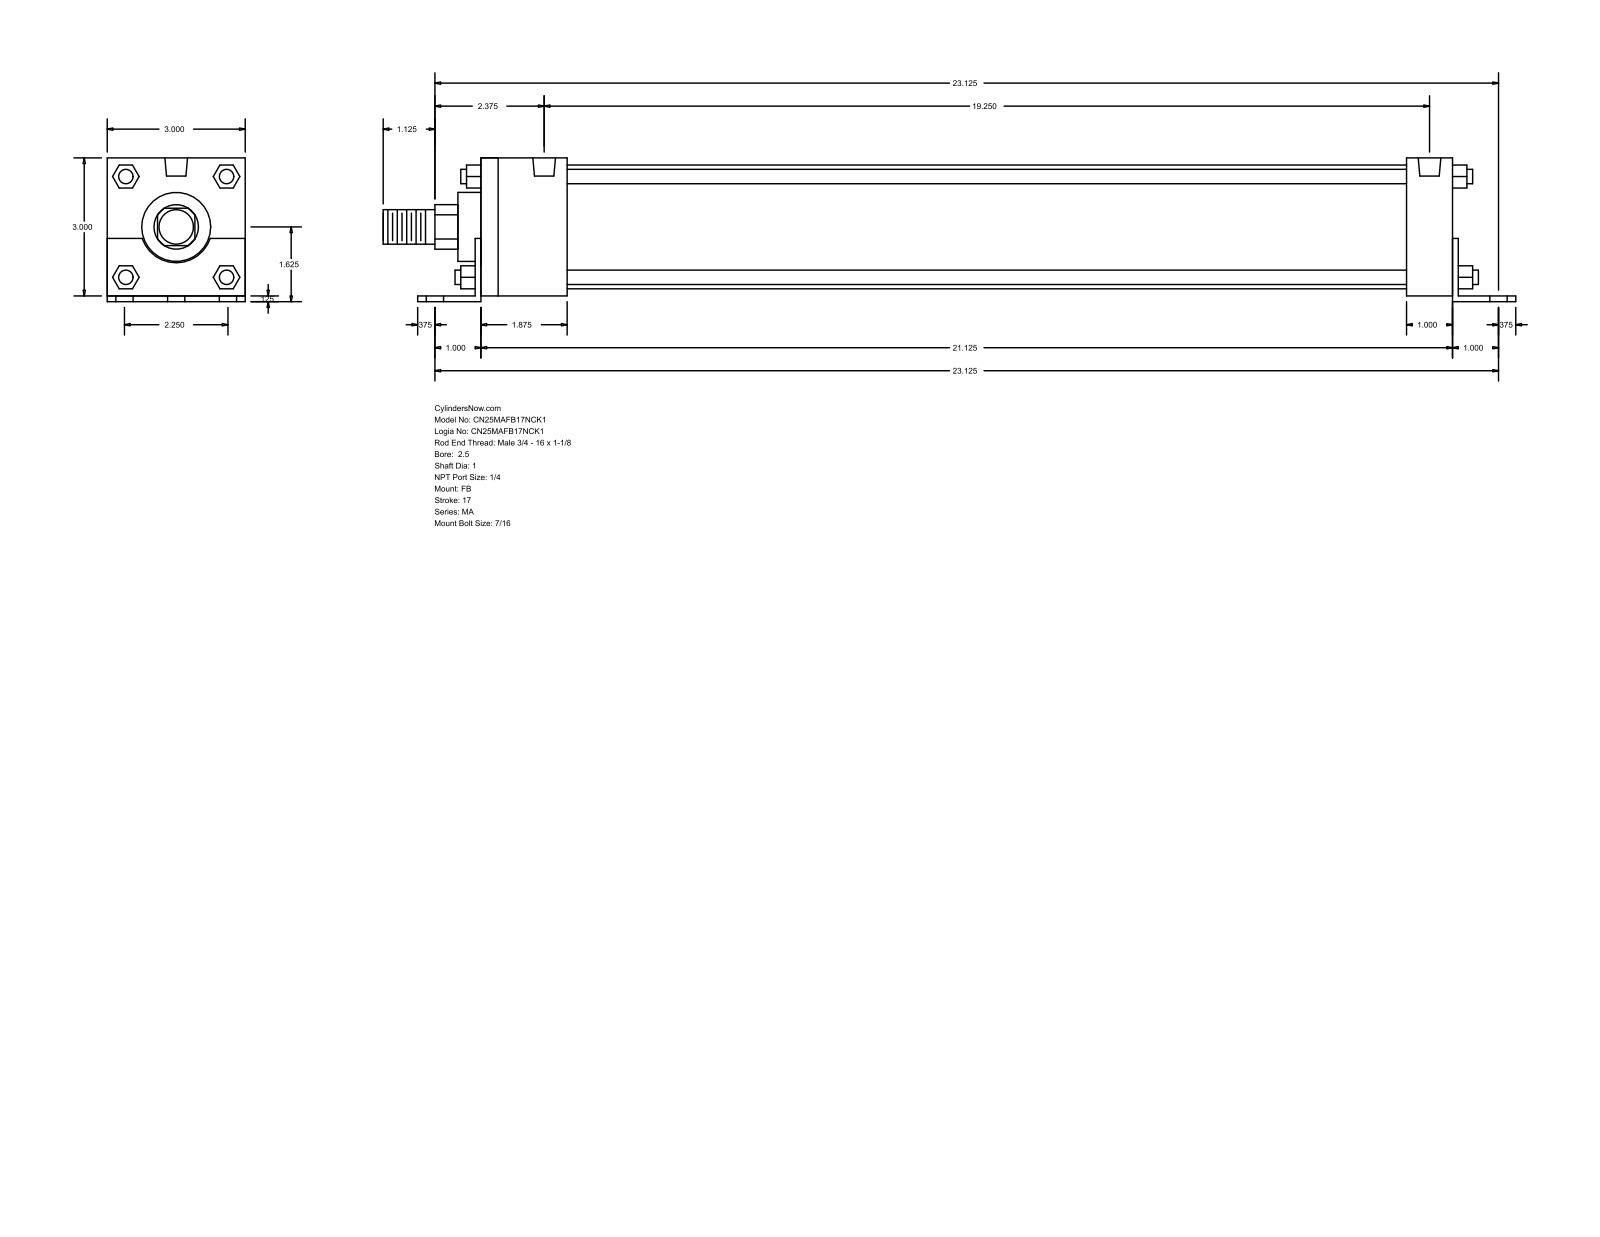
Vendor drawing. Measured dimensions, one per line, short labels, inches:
name: MA_FB__0250_1
written by: GSSL Pune (CONFIG_CONTROL_DESIGN)
unit: in
bodies: 0 solids, 140 faces (105 planar, 35 cylindrical, 0 other)
size: 24.625 × 3.125 × 3
holes: 6× ⌀0.437, 4× ⌀0.313, 2× ⌀0.492
bosses: 4× ⌀0.313, 1× ⌀2.69, 1× ⌀1.5, 1× ⌀1, 1× ⌀0.75
rounds: 1× R0.484, 1× R0.78
face distances: 3, 0.125, 3.125, 21.25, 21.125, 0.5, 1.125, 1, 2, 1.875
hole spacings: 1.125, 23.152, 23.125, 1.875, 2.25, 2.628, 19.25, 20.78
